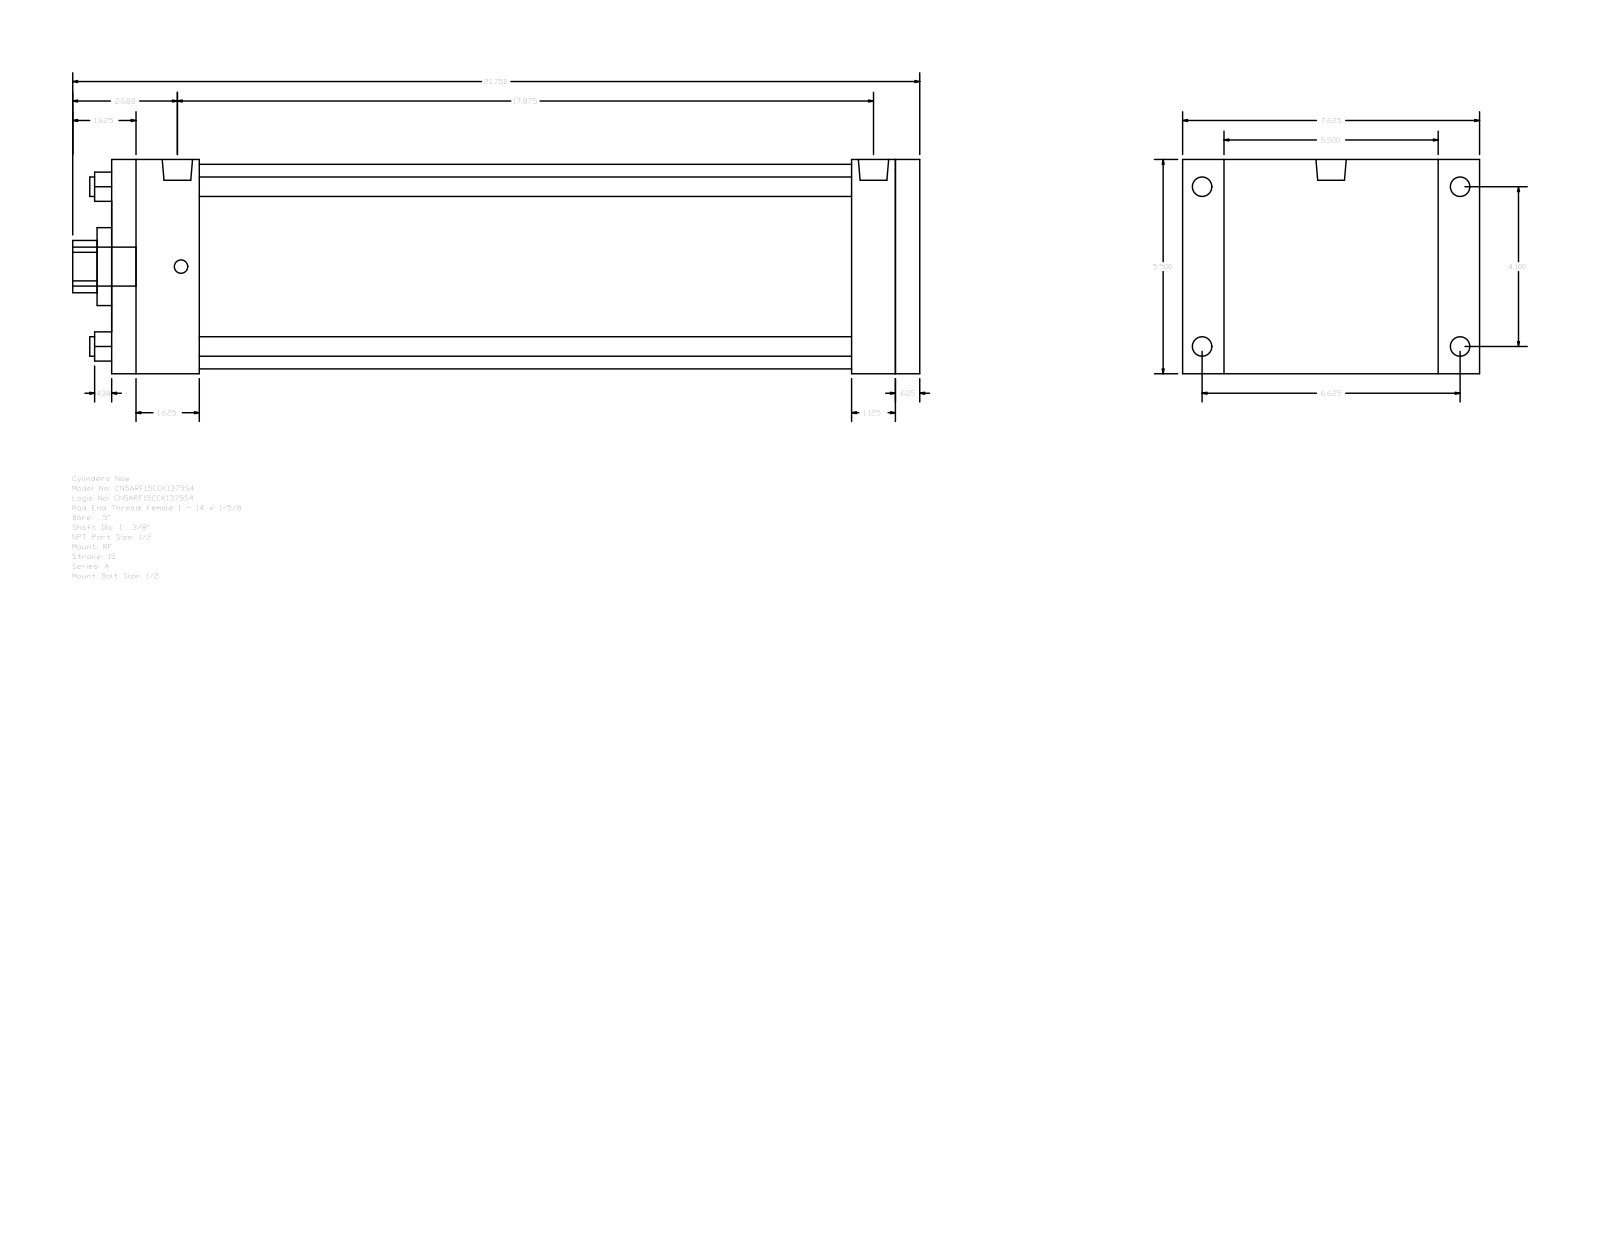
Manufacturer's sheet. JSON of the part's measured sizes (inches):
{"part_name": "A_RF__0500_1.375", "step_written_by": "GSSL Pune (CONFIG_CONTROL_DESIGN)", "units": "inches", "bodies": {"solids": 0, "faces": 92, "planar": 64, "cylindrical": 28, "other": 0}, "overall_size": [21.75, 7.625, 5.5], "round_holes": [[0.5, 4], [1.375, 1], [2, 1], [5.25, 1]], "round_bosses_or_shafts": [[0.5, 4], [0.344, 4], [0.778, 2], [1, 1]], "partial_cylinders_radius": [[0.672, 1]], "face_to_face_distances": [5.5, 20.75, 0.625, 20.125, 1.125, 2.25, 17.875, 18.5, 19, 16.75], "hole_center_spacings": [2.899, 4.1, 5.798]}
